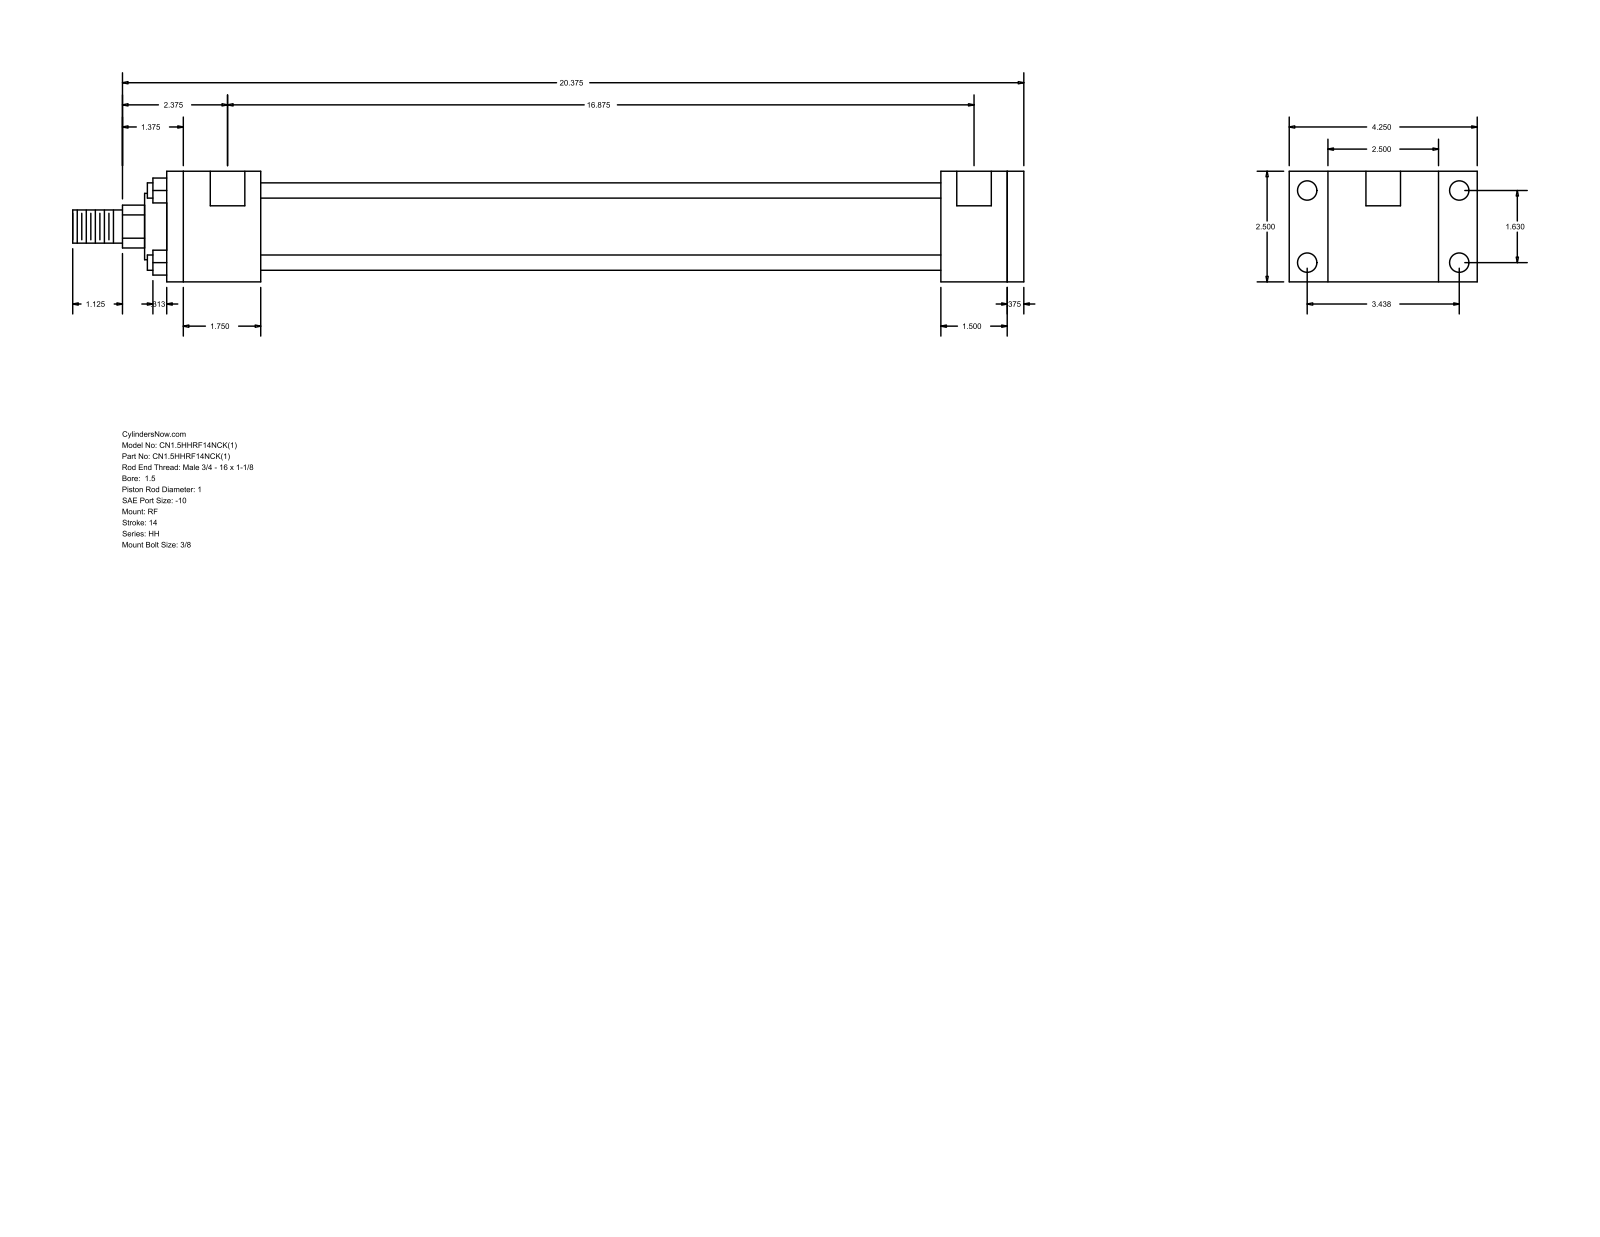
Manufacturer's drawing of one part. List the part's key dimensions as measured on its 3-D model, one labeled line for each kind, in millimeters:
Part name (STEP PRODUCT): HH_RF__0150_1
STEP written by: GSSL Pune (CONFIG_CONTROL_DESIGN)
Units: millimetres
Bodies: 0 solids, 92 faces (64 planar, 28 cylindrical, 0 other)
Overall size (bounding box): 546.1 × 107.95 × 63.5
Round holes (diameter × count): ⌀5.56 ×4, ⌀11.13 ×4, ⌀19.84 ×2
Round bosses / shafts (diameter × count): ⌀8.76 ×4, ⌀44.45 ×1, ⌀38.1 ×1, ⌀25.4 ×1, ⌀19.05 ×1
Partial cylindrical surfaces — rounded edges, fillets, slot ends (radius × count): R12.29 ×1
Main face-to-face distances: 63.5, 9.52, 38.1, 390.52, 428.62, 438.14, 47.62, 53.98, 444.5, 482.6
Hole centre spacings: 1.59, 41.4, 87.32, 96.64, 430.21, 431.8, 428.62
